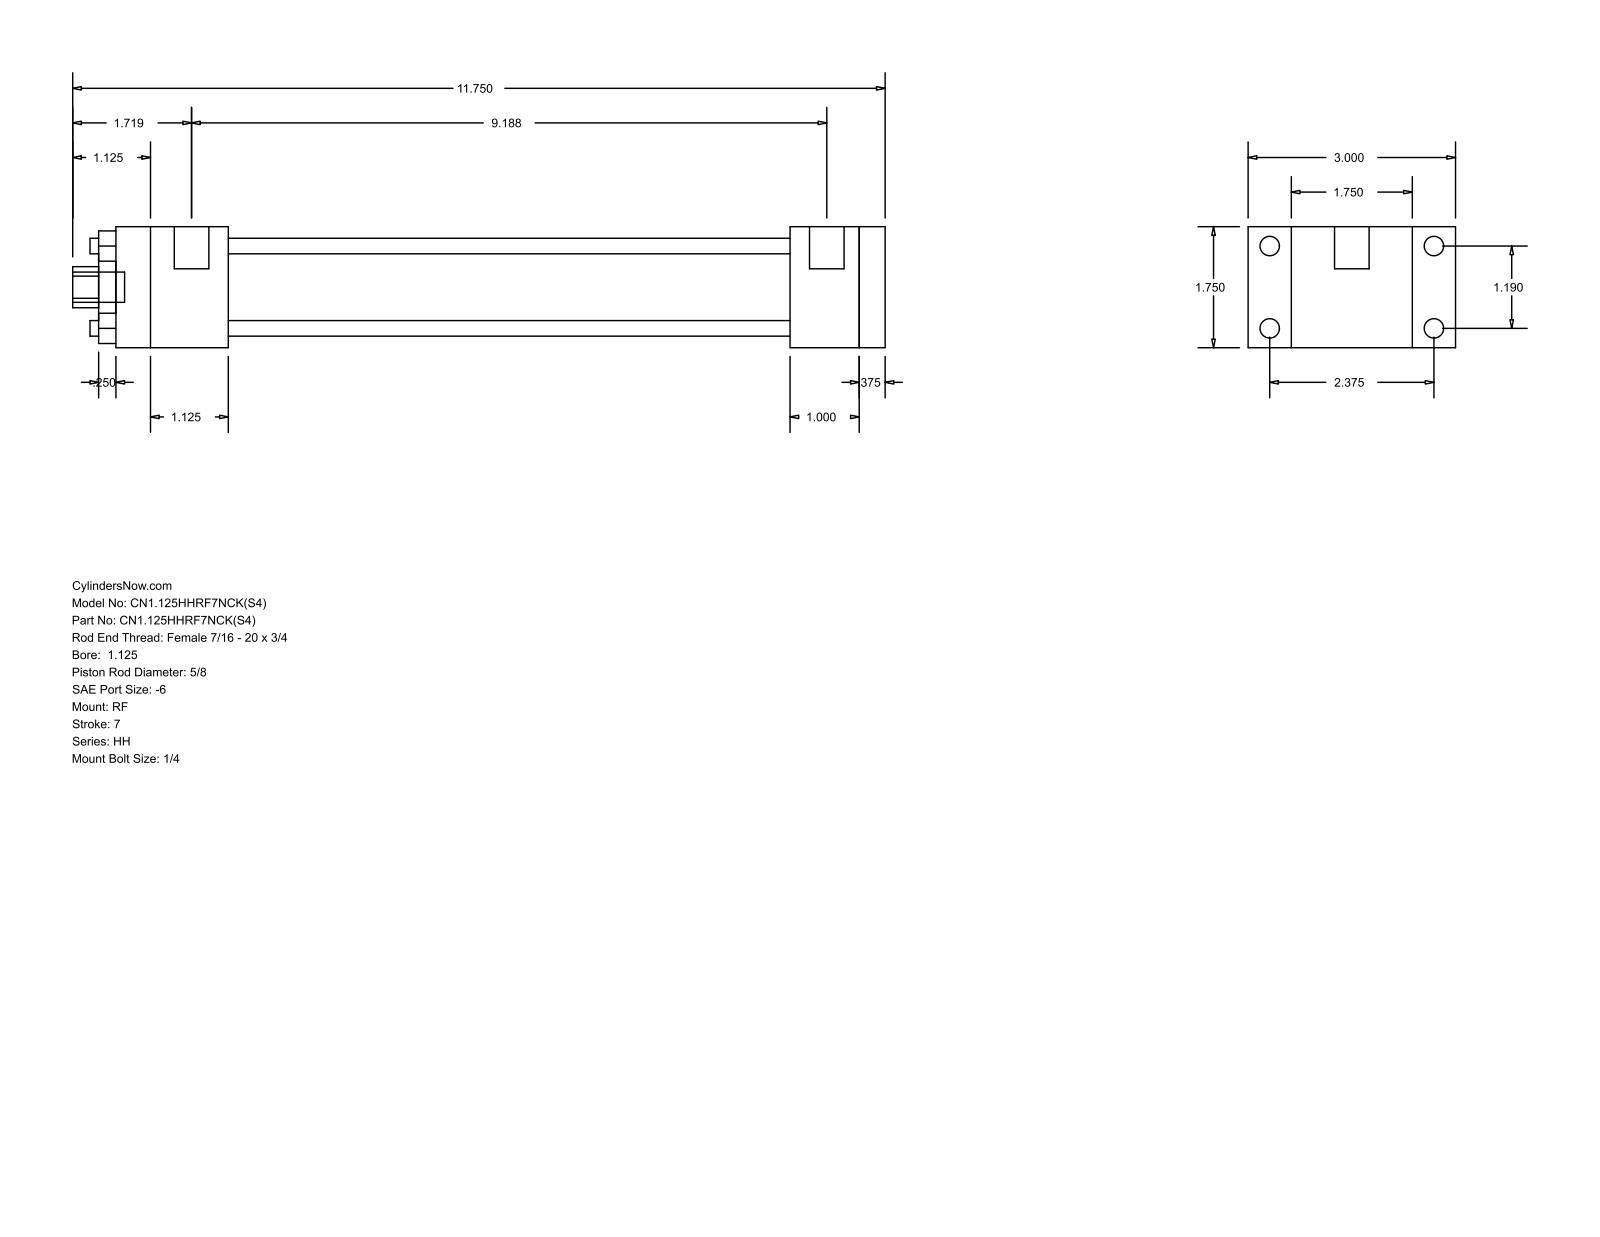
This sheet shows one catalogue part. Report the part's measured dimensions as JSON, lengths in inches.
{"part_name": "HH_RF__0112_0.625", "step_written_by": "GSSL Pune (CONFIG_CONTROL_DESIGN)", "units": "inches", "bodies": {"solids": 0, "faces": 92, "planar": 64, "cylindrical": 28, "other": 0}, "overall_size": [11.75, 3, 1.75], "round_holes": [[0.225, 4], [0.625, 1], [1.125, 1], [1.375, 1]], "round_bosses_or_shafts": [[0.281, 4], [0.219, 4], [0.5, 2], [0.437, 1]], "partial_cylinders_radius": [[0.297, 1]], "face_to_face_distances": [1.75, 0.375, 0.625, 9.125, 9.5, 8.125, 1, 1.375, 1.625, 9.75], "hole_center_spacings": [0.841, 1.19, 1.683]}
